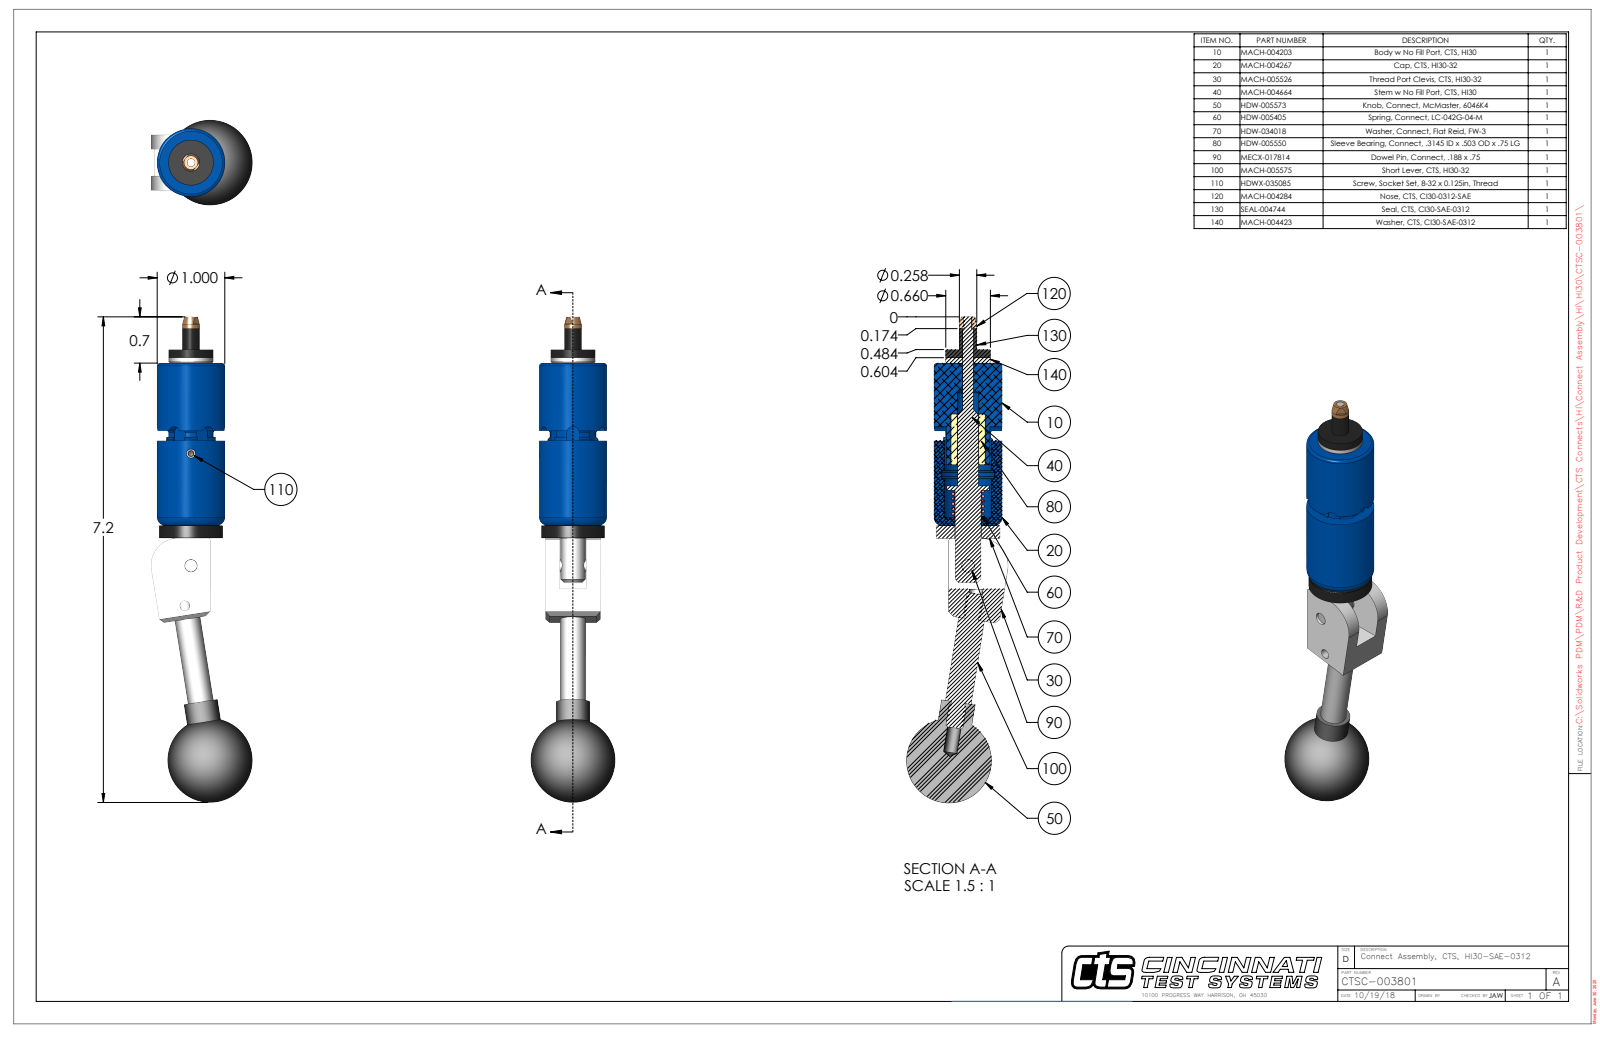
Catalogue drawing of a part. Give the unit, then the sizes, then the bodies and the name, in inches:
Units: inches
Overall size (bounding box): 7.181 × 1.492 × 1.25
Round holes (diameter × count): ⌀0.201 ×2, ⌀0.113 ×1, ⌀0.136 ×1, ⌀0.15 ×1, ⌀0.155 ×1, ⌀0.161 ×1, ⌀0.164 ×1, ⌀0.189 ×1, ⌀0.385 ×1, ⌀0.392 ×1, ⌀0.688 ×1
Round bosses / shafts (diameter × count): ⌀1 ×1, ⌀0.936 ×1, ⌀0.66 ×1, ⌀0.5 ×1, ⌀0.38 ×1, ⌀0.375 ×1, ⌀0.257 ×1, ⌀0.25 ×1
Partial cylindrical surfaces — rounded edges, fillets, slot ends (radius × count): R0.093 ×6, R0.015 ×1, R0.375 ×1, R0.4 ×1, R0.465 ×1
Main face-to-face distances: 0.21, 0.602, 2.4, 0.812, 2.587, 0.187, 0.08, 2.48, 2.667, 0.391
Hole centre spacings: 0.599, 1.658, 2.252
Volume: 3.834 in³ · Surface area: 30.66 in²
Bodies: 10 solids, 268 faces (99 planar, 110 cylindrical, 59 other)
Part name (STEP PRODUCT): CTSC-003801
STEP written by: SolidWorks 2023 (AUTOMOTIVE_DESIGN)
